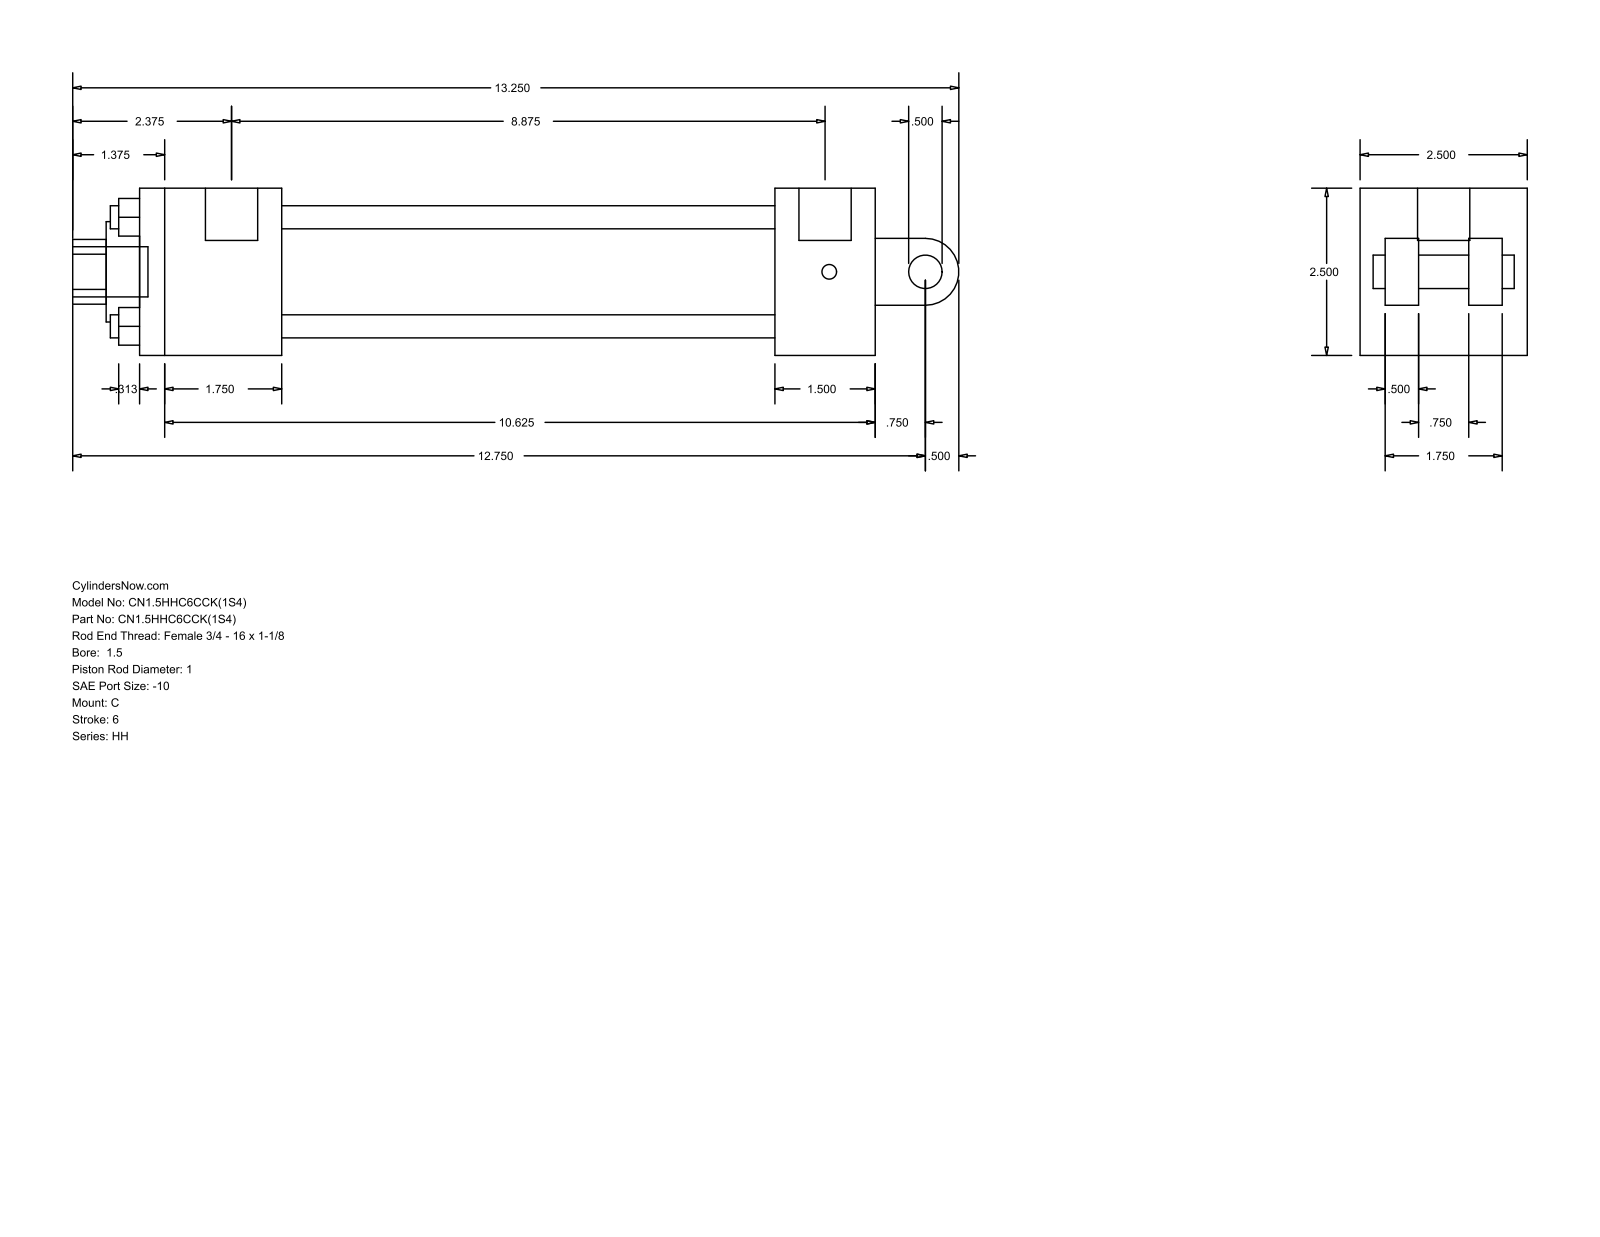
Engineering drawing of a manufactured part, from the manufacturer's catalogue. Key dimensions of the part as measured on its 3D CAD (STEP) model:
Part name (STEP PRODUCT): HH_C__0150_1
STEP written by: GSSL Pune (CONFIG_CONTROL_DESIGN)
Units: millimetres
Bodies: 0 solids, 99 faces (70 planar, 29 cylindrical, 0 other)
Overall size (bounding box): 336.55 × 63.5 × 63.5
Round holes (diameter × count): ⌀8.76 ×4, ⌀5.56 ×2, ⌀19.84 ×1, ⌀25.4 ×1, ⌀38.1 ×1, ⌀44.45 ×1
Round bosses / shafts (diameter × count): ⌀5.56 ×2, ⌀19.84 ×1, ⌀19.05 ×1, ⌀12.7 ×1
Partial cylindrical surfaces — rounded edges, fillets, slot ends (radius × count): R12.29 ×1, R12.7 ×1
Main face-to-face distances: 63.5, 53.98, 187.32, 225.42, 38.1, 241.3, 279.4, 12.7, 22.22, 41.28
Hole centre spacings: 29.27, 41.4, 58.55, 1.59
